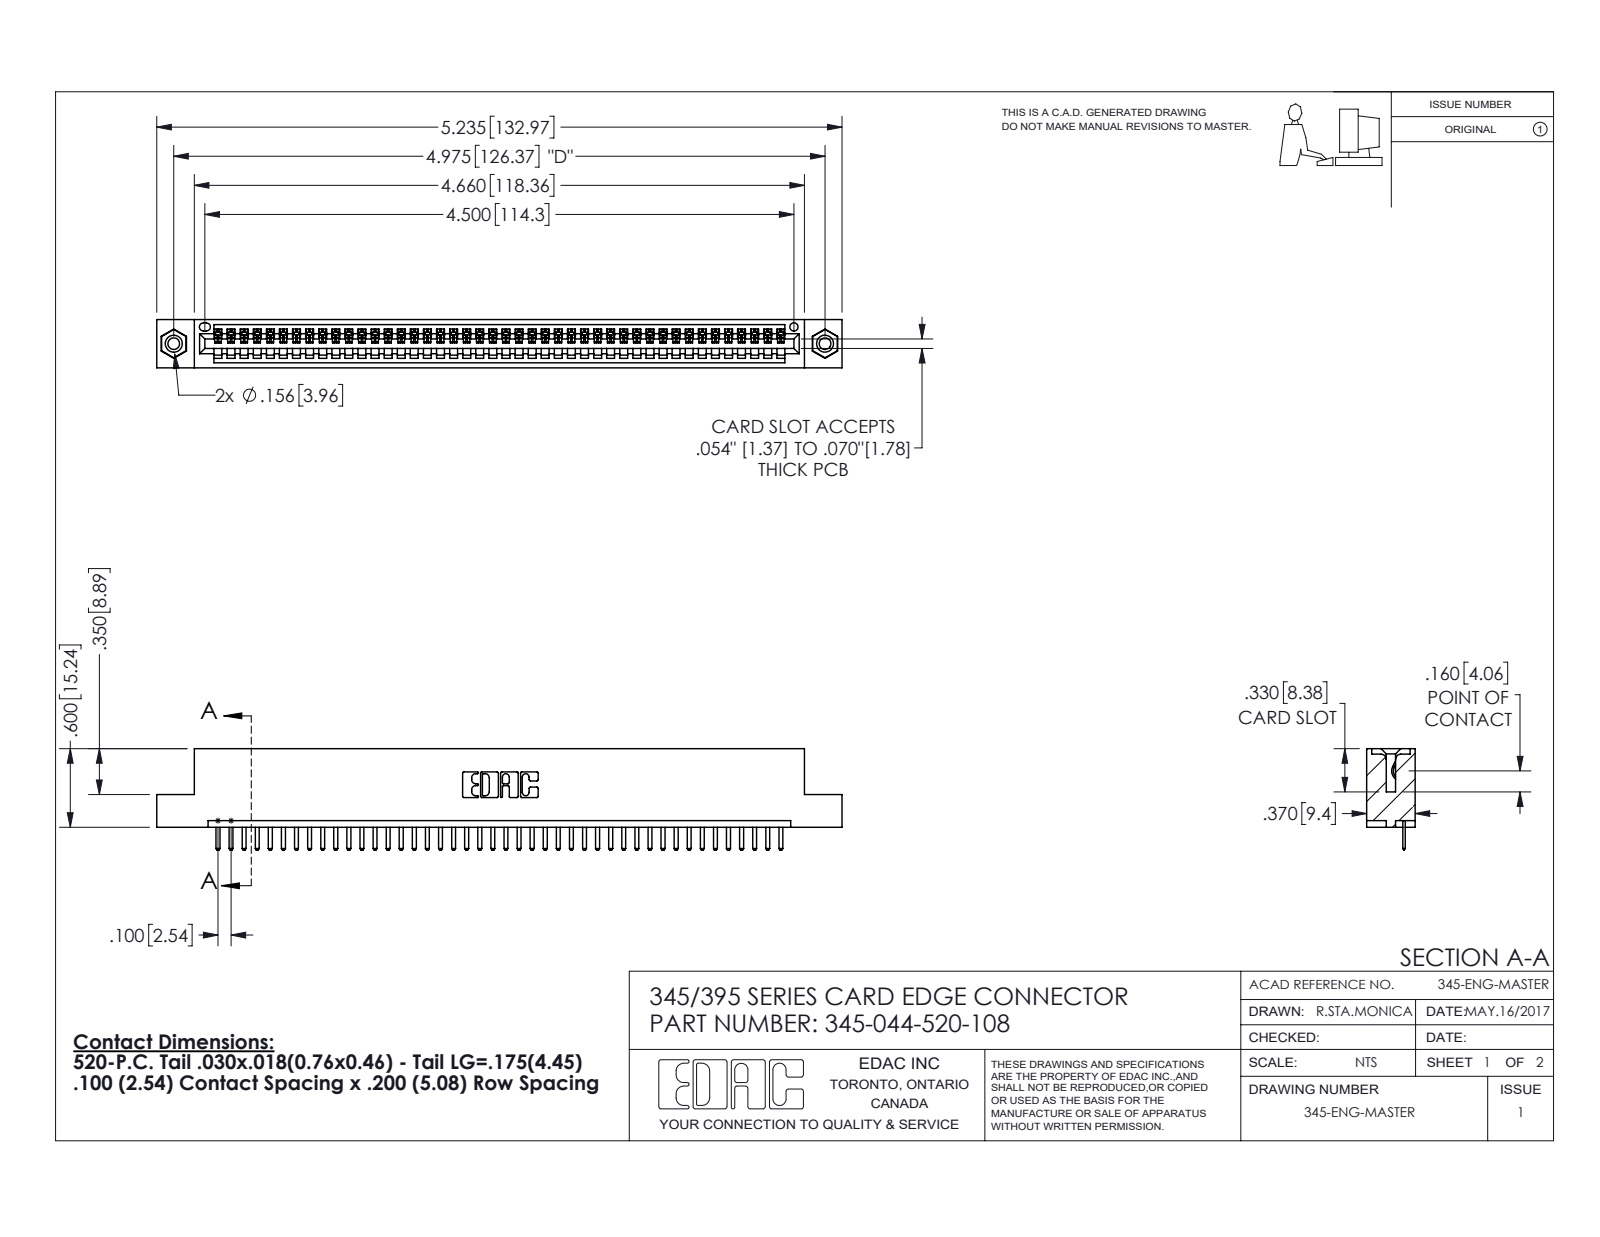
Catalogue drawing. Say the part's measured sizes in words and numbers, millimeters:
The part is named "345-292-001_345-293-120; 345-250-001_345-250-003-102; 345-044-520-108; 345 Part_Flush Mounting Lugs - 0.156 Dia-TI". Its 3-D file was written by "SolidWorks 2016 (CONFIG_CONTROL_DESIGN)". It is 47 solids with 2914 faces: 1960 planar, 938 cylindrical and 16 other. Overall it measures 133 by 19.7 by 9.4 millimeters. Its volume is 12 500 cubic millimeters and its surface area 16 260 square millimeters. Round holes: 2 of diameter 2.3, 2 of diameter 3.2, 2 of diameter 4, 1 of diameter 1.6. Round bosses or shafts: 2 of diameter 3.9. Partial cylindrical surfaces (rounded edges, fillets, slot ends): 90 of radius 0.3, 88 of radius 0.2, 22 of radius 0.3, 6 of radius 0.2, 6 of radius 0.8, 3 of radius 0.7, 2 of radius 0.8, 2 of radius 1. The main face-to-face distances are 1.8, 7.6, 9.4, 5.1, 2.5, 6.9, 0.6, 5.7, 1.8, 3.8. The hole center spacings are 6.9, 120.4, 126.4.
